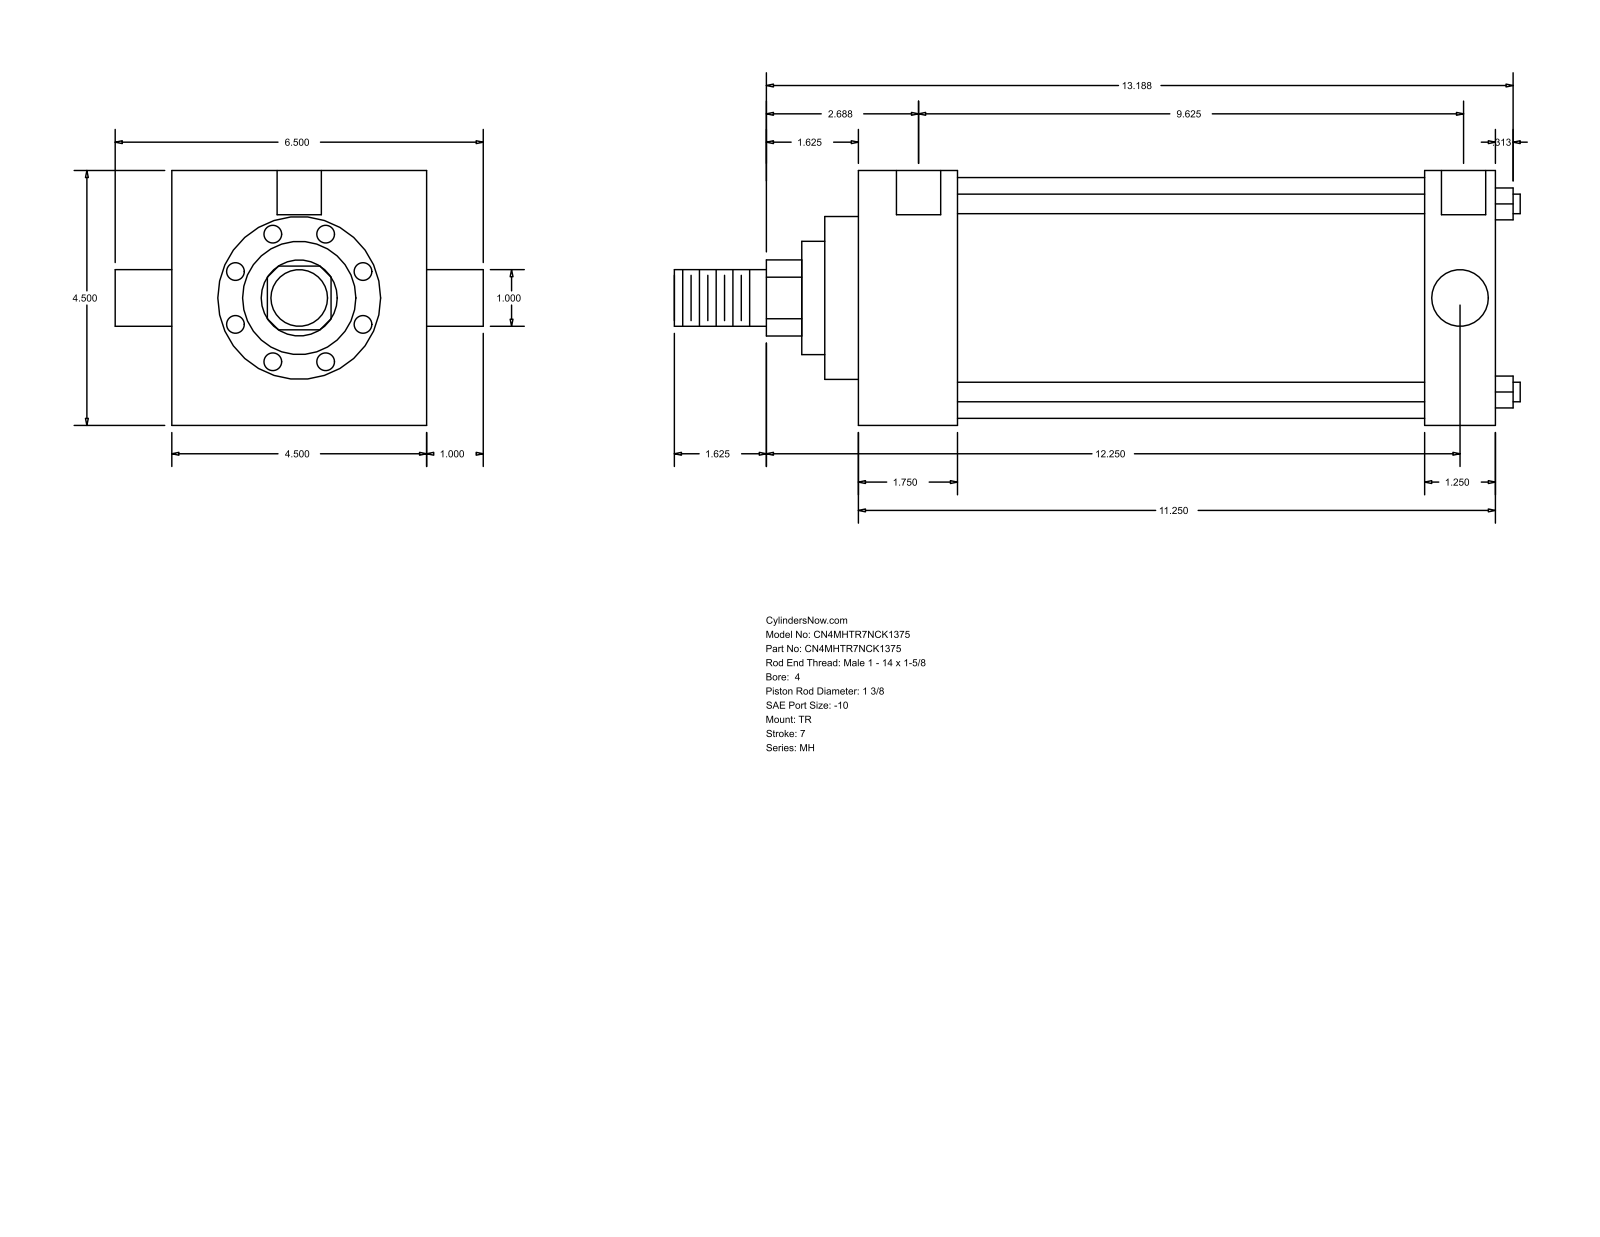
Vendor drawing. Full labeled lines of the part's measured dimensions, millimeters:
Part name (STEP PRODUCT): MH_TR__0400_1.375
STEP written by: GSSL Pune (CONFIG_CONTROL_DESIGN)
Units: millimetres
Bodies: 0 solids, 86 faces (61 planar, 25 cylindrical, 0 other)
Overall size (bounding box): 379.41 × 165.1 × 114.3
Round holes (diameter × count): ⌀8.73 ×3, ⌀19.84 ×2
Round bosses / shafts (diameter × count): ⌀8.76 ×4, ⌀25.4 ×2, ⌀107.95 ×1, ⌀73.03 ×1, ⌀50.8 ×1, ⌀34.92 ×1
Partial cylindrical surfaces — rounded edges, fillets, slot ends (radius × count): R17.06 ×1
Main face-to-face distances: 114.3, 285.75, 44.45, 241.3, 254, 209.55, 31.75, 15.08, 59.53, 269.08
Hole centre spacings: 1.58, 1.59, 244.48, 246.06, 246.07, 247.65
